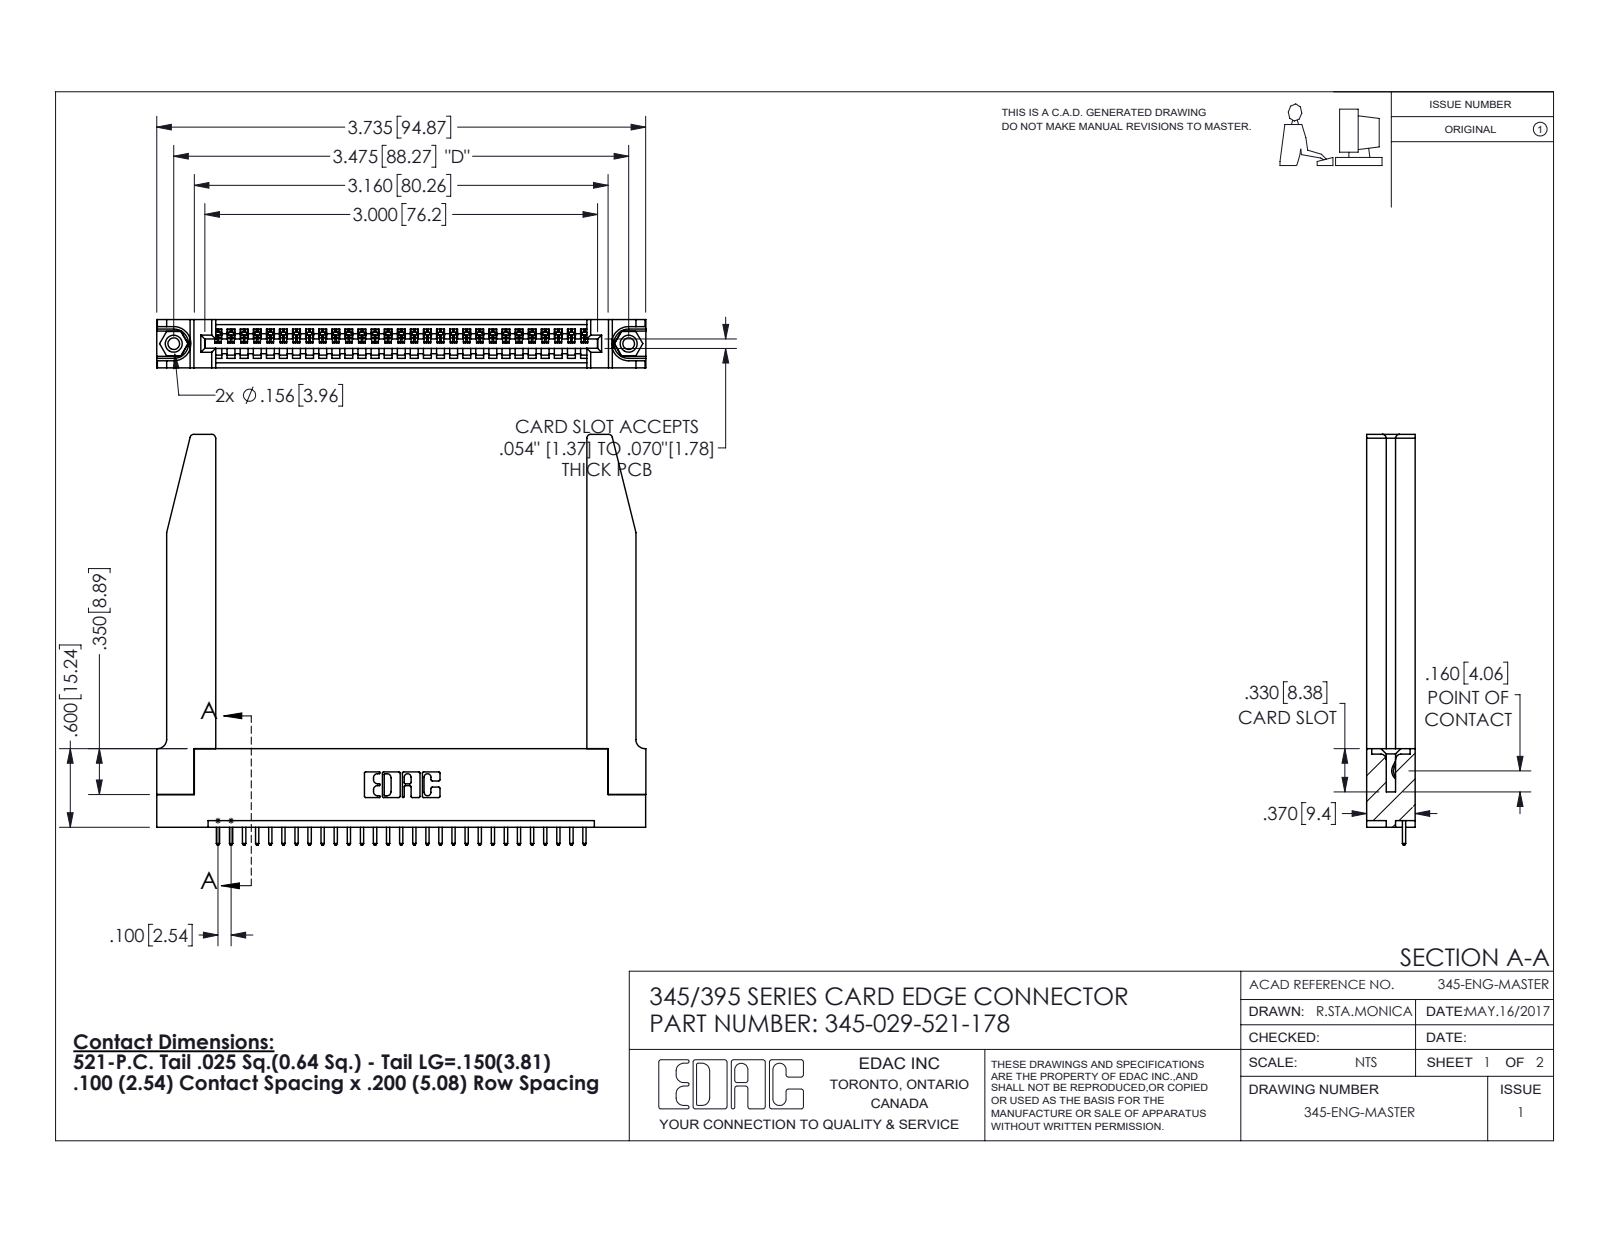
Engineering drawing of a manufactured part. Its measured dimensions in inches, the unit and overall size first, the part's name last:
Units: inches
Overall size (bounding box): 3.736 × 3.137 × 0.37
Round holes (diameter × count): ⌀0.089 ×2, ⌀0.125 ×2, ⌀0.156 ×2, ⌀0.064 ×1
Round bosses / shafts (diameter × count): ⌀0.155 ×2
Partial cylindrical surfaces — rounded edges, fillets, slot ends (radius × count): R0.006 ×58, R0.01 ×58, R0.01 ×22, R0.03 ×8, R0.007 ×6, R0.031 ×6, R0.026 ×3, R0.031 ×2
Main face-to-face distances: 0.37, 0.072, 0.298, 0.2, 0.098, 0.272, 0.025, 0.148, 0.15, 0.225
Hole centre spacings: 0.27, 3.24, 3.475
Volume: 1.013 in³ · Surface area: 28.01 in²
Bodies: 34 solids, 2042 faces (1382 planar, 608 cylindrical, 52 other)
Part name (STEP PRODUCT): 345-029-521-178; 345-220-078_345-220-078; 345-292-001_345-293-121; 345 Part_Flush Mounting Lugs - 0.156 Dia-TH (+1 more)
STEP written by: SolidWorks 2016 (CONFIG_CONTROL_DESIGN)
